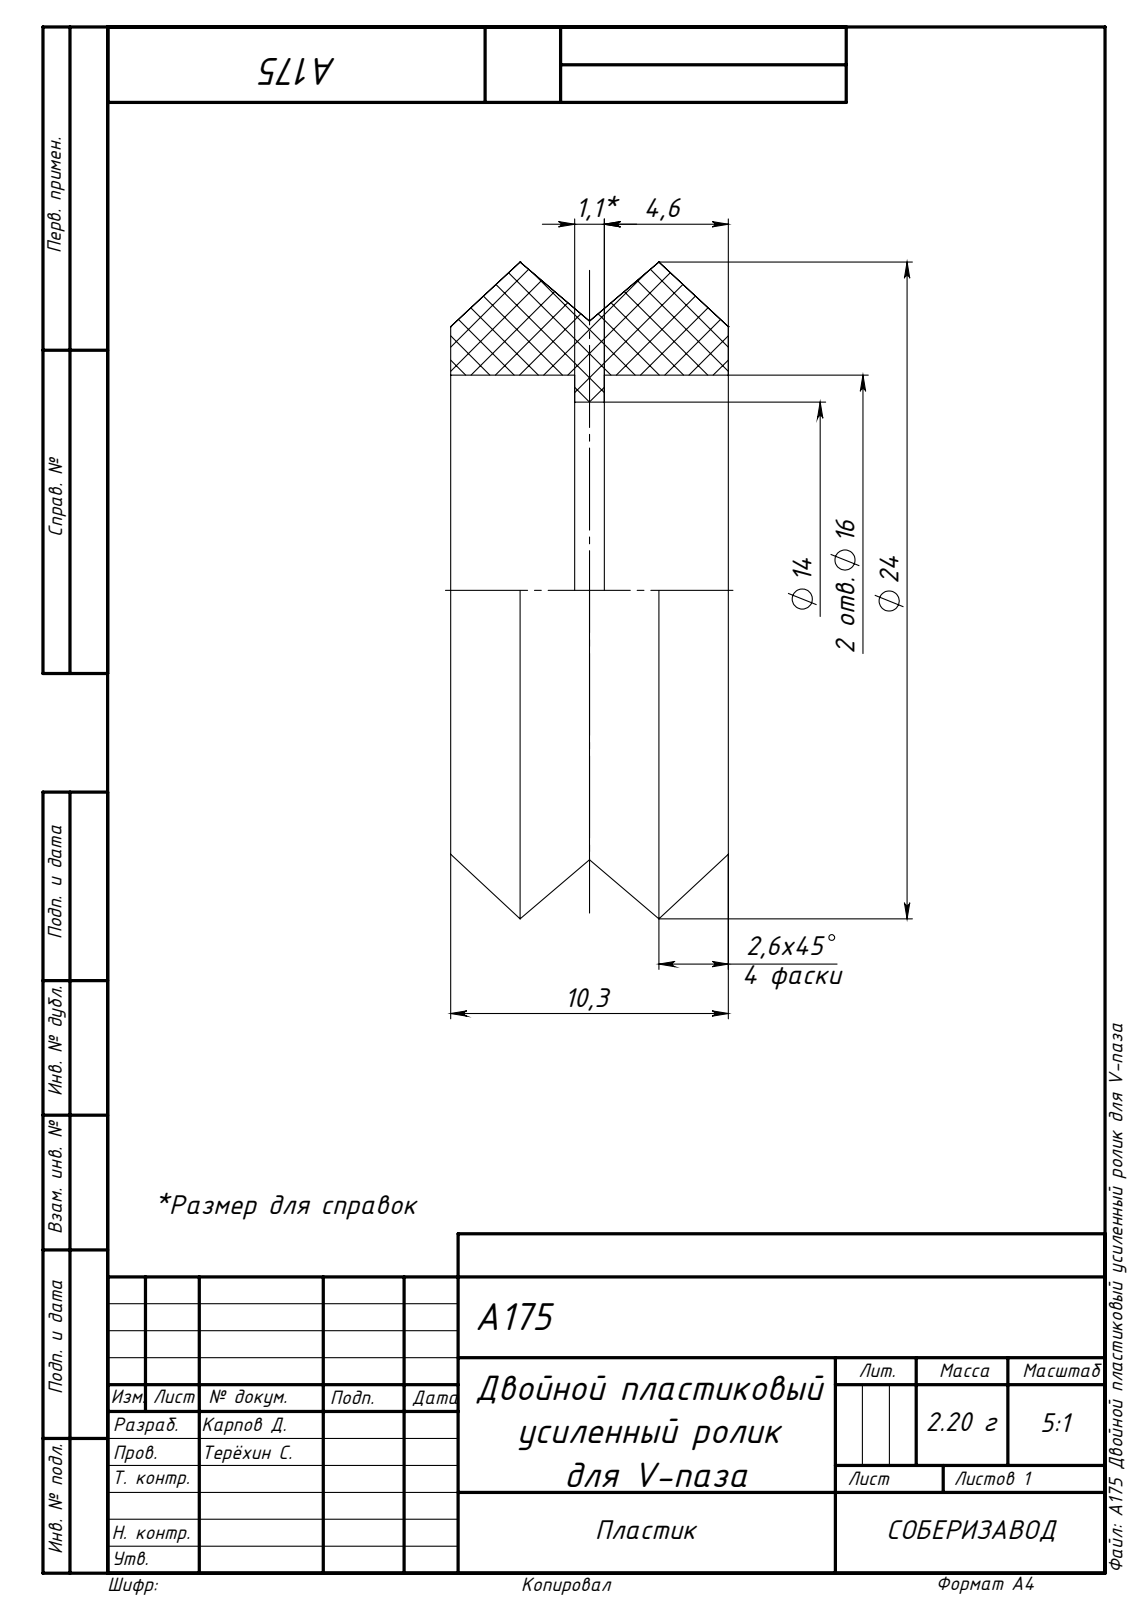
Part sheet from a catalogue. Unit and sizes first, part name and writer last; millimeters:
Units: millimetres
Overall size (bounding box): 24.39 × 24.39 × 10.3
Round holes (diameter × count): ⌀13.99 ×1, ⌀15.99 ×1
Main face-to-face distances: 10.3, 4.6, 5.7, 1.1
Volume: 1 946 mm³ · Surface area: 1 764 mm²
Bodies: 1 solid, 18 faces (4 planar, 6 cylindrical, 8 other)
STEP written by: SolidWorks 2018 (AUTOMOTIVE_DESIGN)
